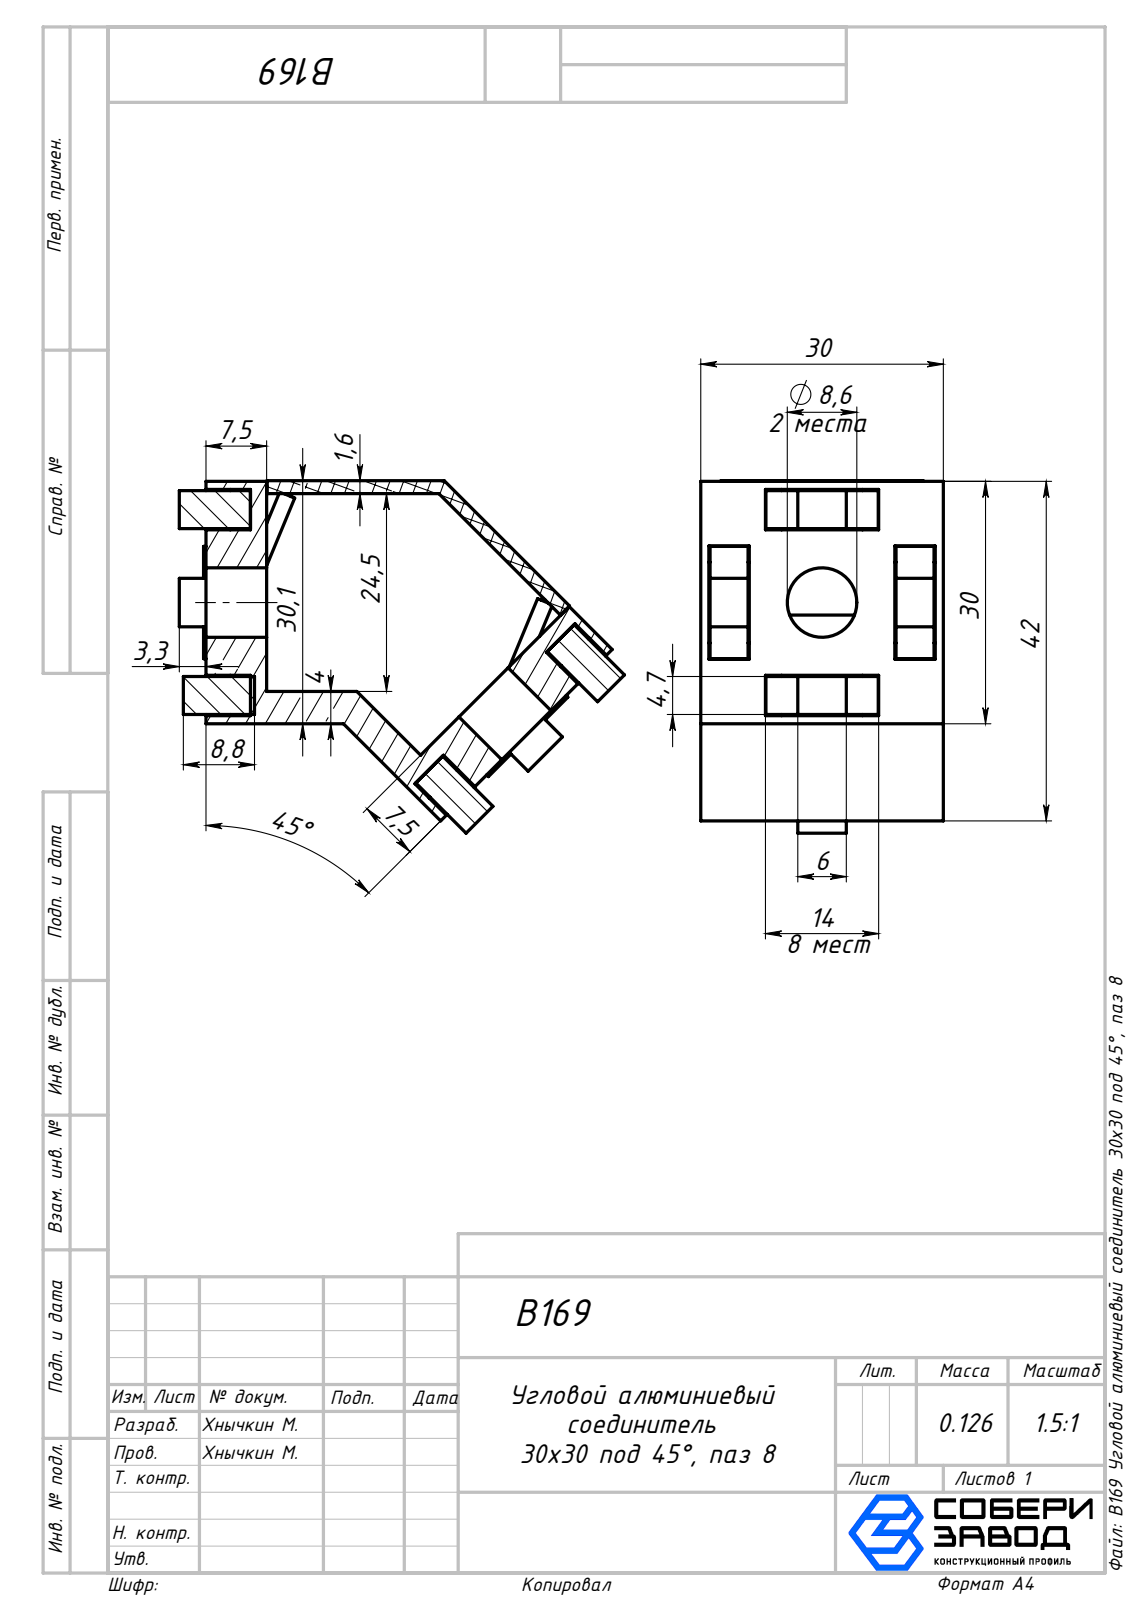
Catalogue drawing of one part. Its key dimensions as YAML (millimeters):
part_name: "B169 Угловой алюминиевый соединитель 30х30 под 45°, паз 8; B169 Корпус_00; B169 Крышка_00; B169 Внтурнний сухарь_00"
step_written_by: "SolidWorks 2025 (AUTOMOTIVE_DESIGN)"
units: millimeters
bodies: {solids: 10, faces: 254, planar: 230, cylindrical: 24, other: 0}
overall_size: [55.05, 43.62, 30]
volume: 21499
surface_area: 17068
round_holes:
  - {diameter: 3.2, count: 4}
  - {diameter: 8.6, count: 2}
round_bosses_or_shafts:
  - {diameter: 3, count: 4}
partial_cylinders:
  - {radius: 2, count: 4}
face_to_face_distances: [2.5, 27.5, 30, 6, 2, 7.5, 1.6, 28.48, 30.08, 4]
hole_center_spacings: [21, 36.5, 42.11]
